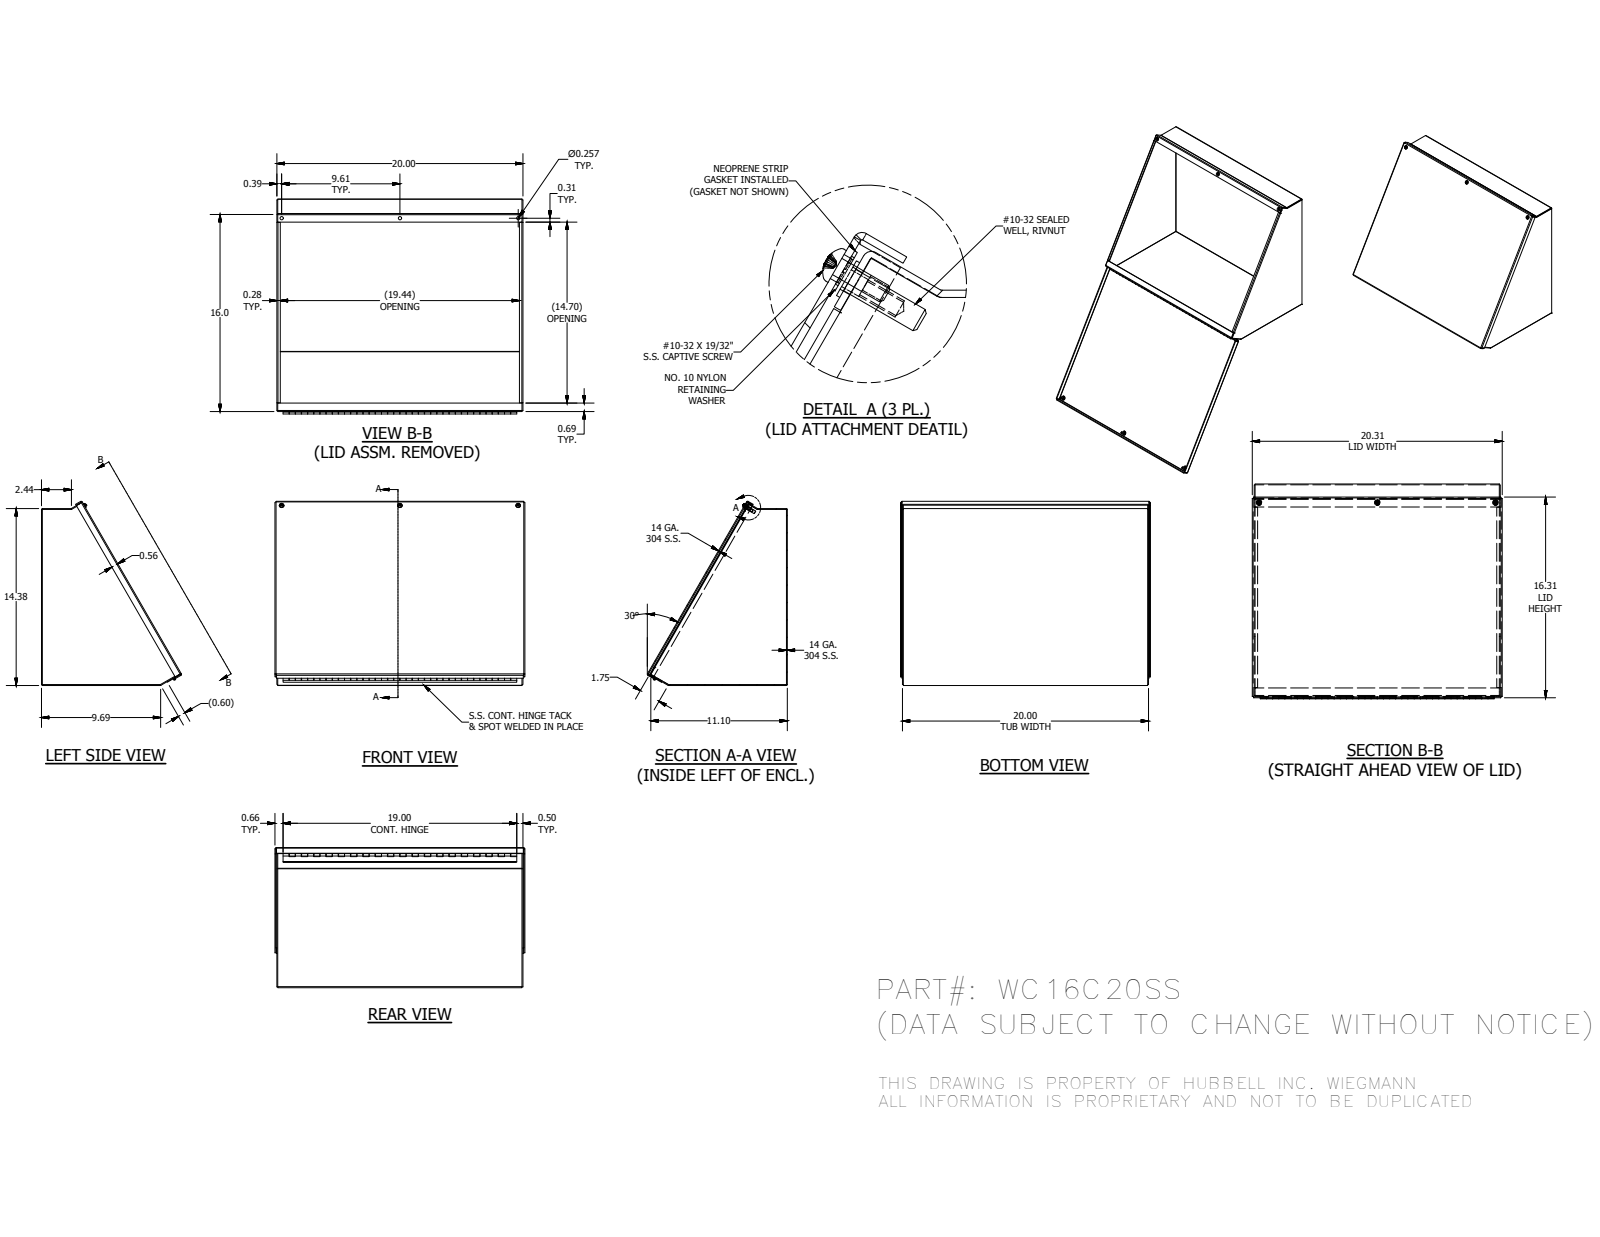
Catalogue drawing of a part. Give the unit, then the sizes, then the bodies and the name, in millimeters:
Units: millimetres
Overall size (bounding box): 515.94 × 380 × 289.23
Round holes (diameter × count): ⌀3.96 ×3, ⌀4.98 ×3, ⌀6.53 ×3, ⌀7.06 ×3, ⌀7.14 ×3, ⌀2.96 ×1
Round bosses / shafts (diameter × count): ⌀11.51 ×3, ⌀10.31 ×3, ⌀9.47 ×3, ⌀6.3 ×3, ⌀4.83 ×3, ⌀5.08 ×1, ⌀2.54 ×1
Partial cylindrical surfaces — rounded edges, fillets, slot ends (radius × count): R0.4 ×12, R2.28 ×12, R2.27 ×3
Main face-to-face distances: 1.88, 506.12, 504.24, 508, 363.25, 361.37, 1.87, 365.12, 363.24, 2.94
Hole centre spacings: 244.17, 488.34, 1.41
Volume: 1 455 000 mm³ · Surface area: 1 582 000 mm²
Bodies: 16 solids, 557 faces (340 planar, 143 cylindrical, 74 other)
Part name (STEP PRODUCT): WC16C20SSBTB; WC16C20SSLID; WC16CSSLS; WC16CSSRS (+8 more)
STEP written by: Autodesk Inventor 2014 (AUTOMOTIVE_DESIGN)
